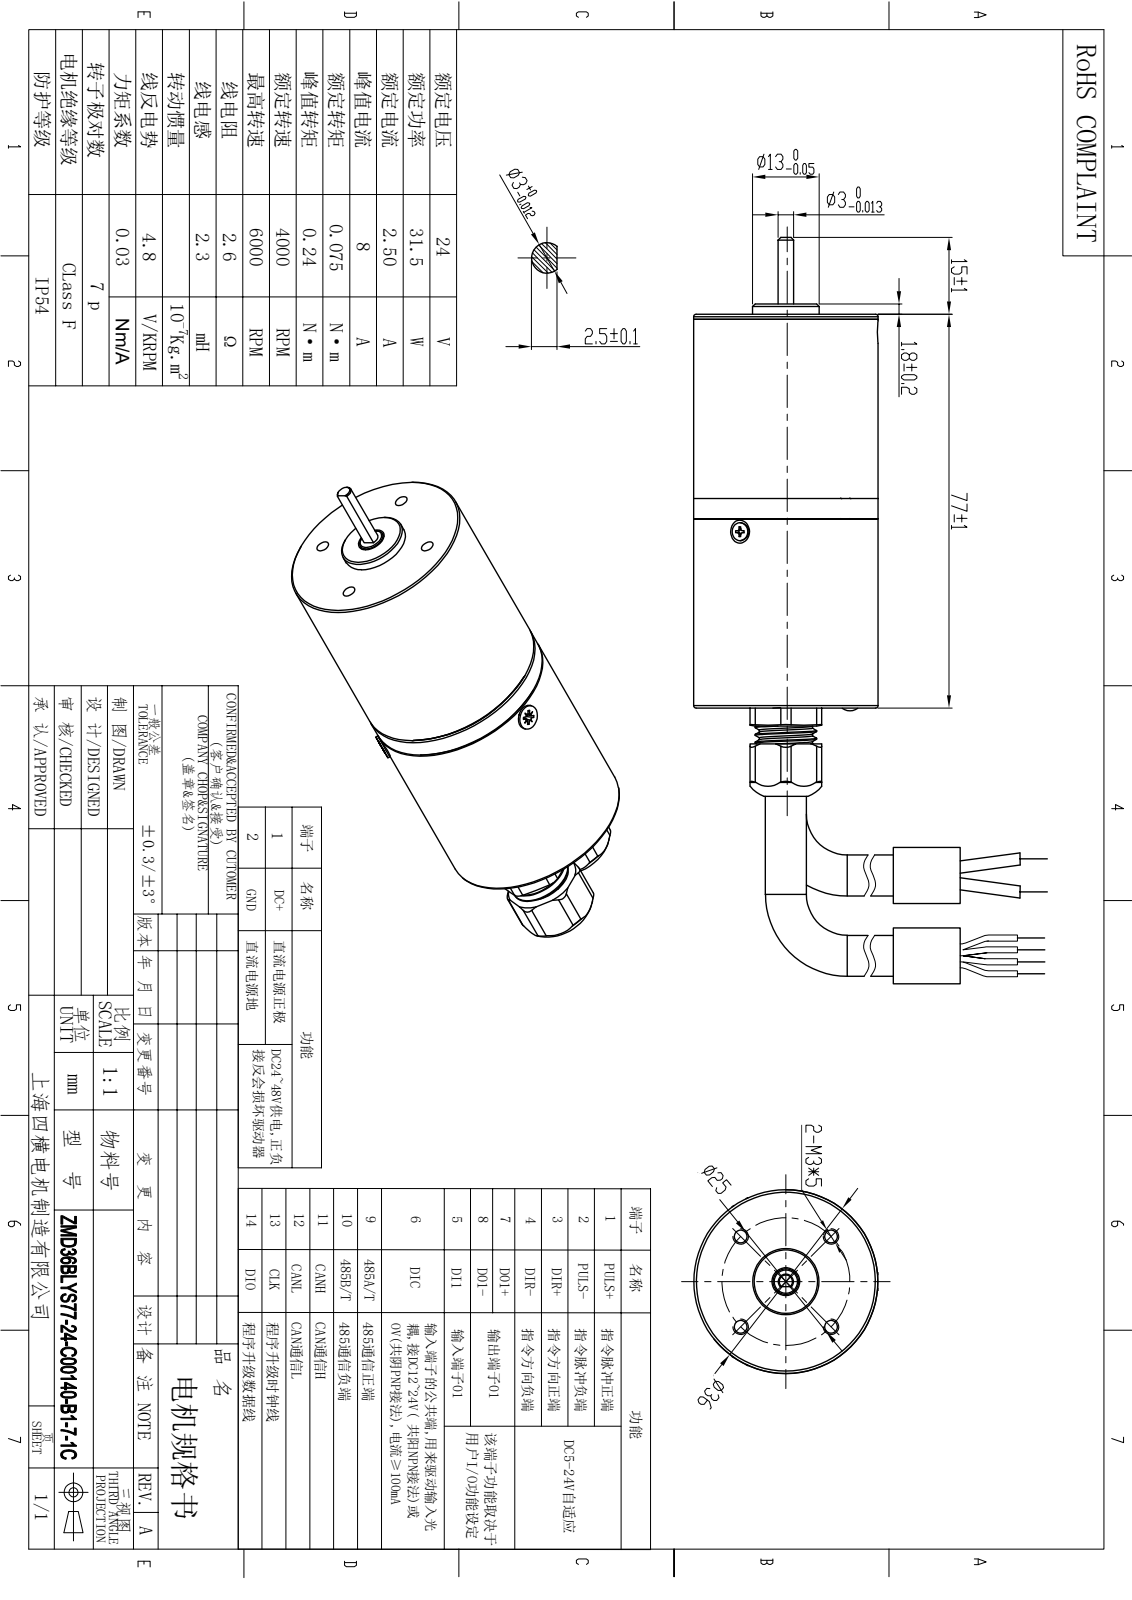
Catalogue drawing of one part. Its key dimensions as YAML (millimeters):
part_name: "ZMD36BLYS77-24-C00140-B1-7-1C"
step_written_by: "SolidWorks 2020 (CONFIG_CONTROL_DESIGN)"
units: millimeters
bodies: {solids: 10, faces: 338, planar: 98, cylindrical: 101, other: 139}
overall_size: [109.23, 36.49, 36.49]
volume: 40006
surface_area: 28983
round_holes:
  - {diameter: 2.05, count: 7}
  - {diameter: 2.5, count: 4}
  - {diameter: 2.9, count: 4}
  - {diameter: 5, count: 4}
  - {diameter: 1.6, count: 3}
  - {diameter: 8.2, count: 2}
  - {diameter: 8.35, count: 2}
  - {diameter: 8.5, count: 2}
  - {diameter: 3, count: 1}
  - {diameter: 5.5, count: 1}
  - {diameter: 6, count: 1}
  - {diameter: 16, count: 1}
round_bosses_or_shafts:
  - {diameter: 4.7, count: 3}
  - {diameter: 2.5, count: 3}
  - {diameter: 12, count: 2}
  - {diameter: 10, count: 2}
  - {diameter: 2.16, count: 2}
  - {diameter: 36, count: 1}
  - {diameter: 34, count: 1}
  - {diameter: 20, count: 1}
partial_cylinders:
  - {radius: 2, count: 12}
  - {radius: 1, count: 2}
  - {radius: 15.5, count: 1}
face_to_face_distances: [34, 40, 37, 3, 42, 77, 5, 39, 35, 4]
hole_center_spacings: [19.14, 2, 12.5, 14.5, 17.68, 20.51, 27, 3.53]
